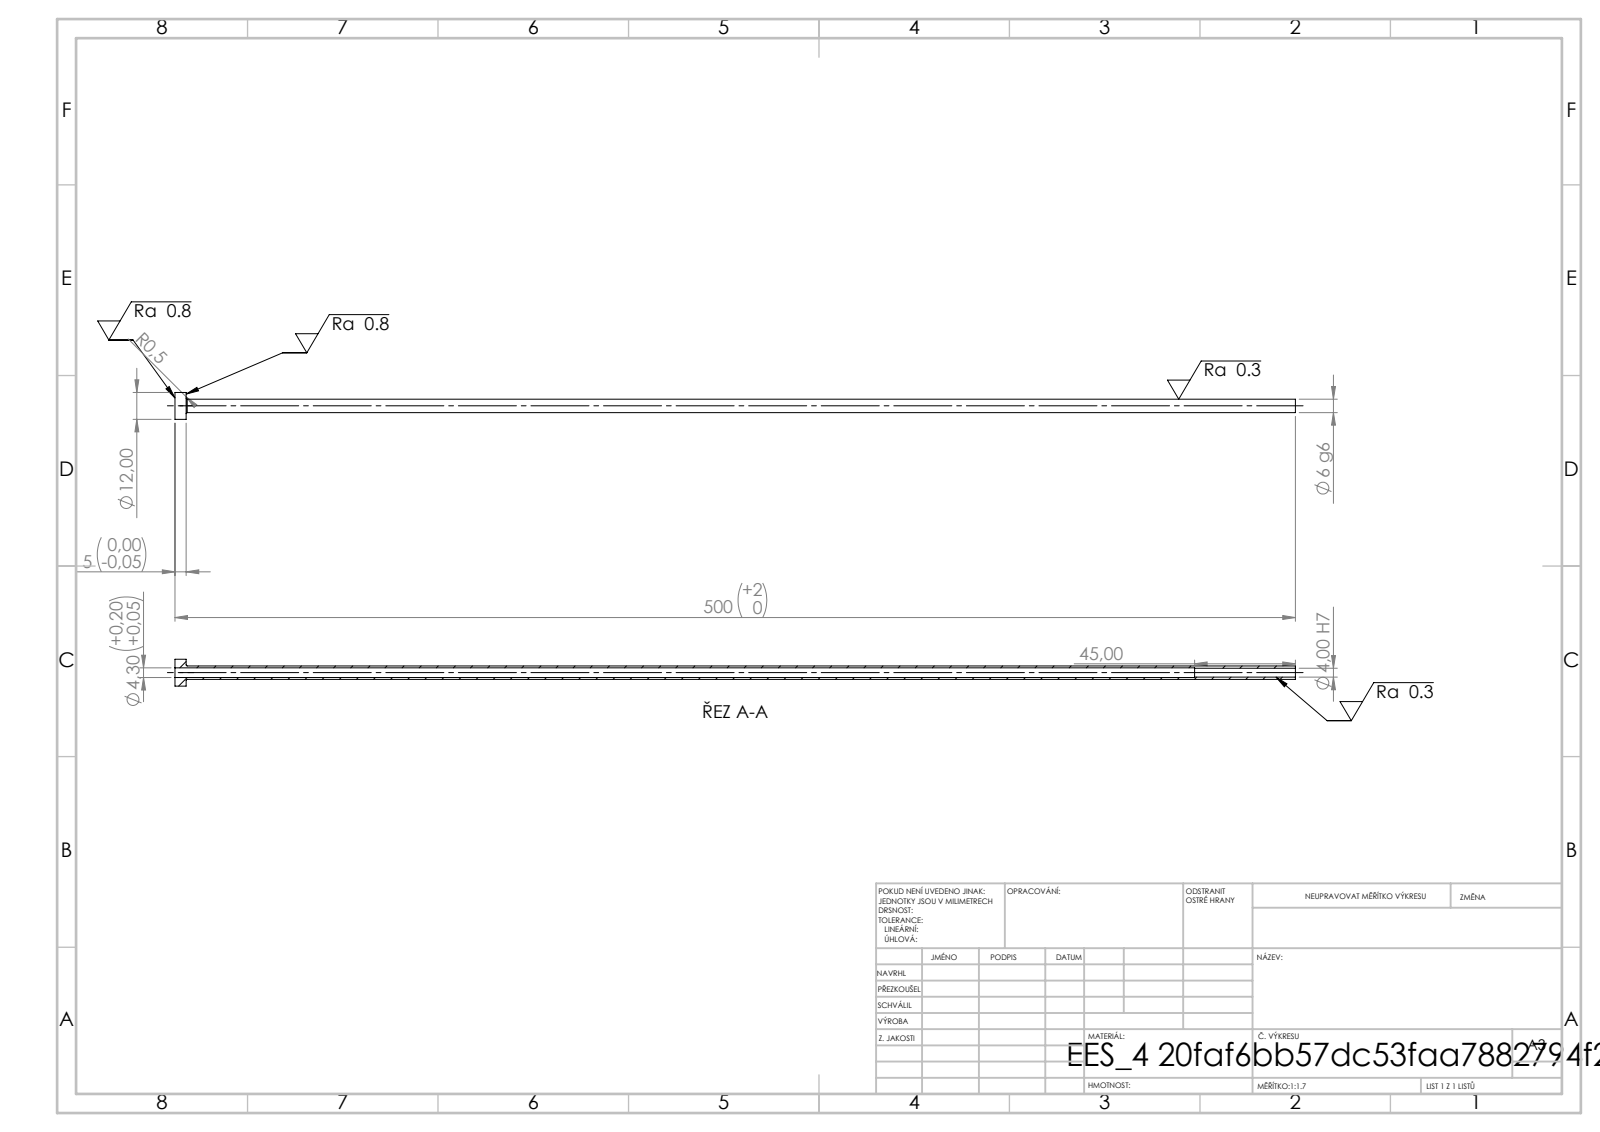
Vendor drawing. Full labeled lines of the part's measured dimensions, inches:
STEP written by: SolidWorks 2019 (CONFIG_CONTROL_DESIGN)
Units: inches
Bodies: 1 solid, 14 faces (4 planar, 8 cylindrical, 2 other)
Overall size (bounding box): 19.685 × 0.472 × 0.472
Volume: 0.451 in³ · Surface area: 25.46 in²
Round holes (diameter × count): ⌀0.157 ×1, ⌀0.169 ×1
Round bosses / shafts (diameter × count): ⌀0.472 ×1, ⌀0.236 ×1
Main face-to-face distances: 0.197, 19.685, 19.488, 17.913, 17.717, 1.772
